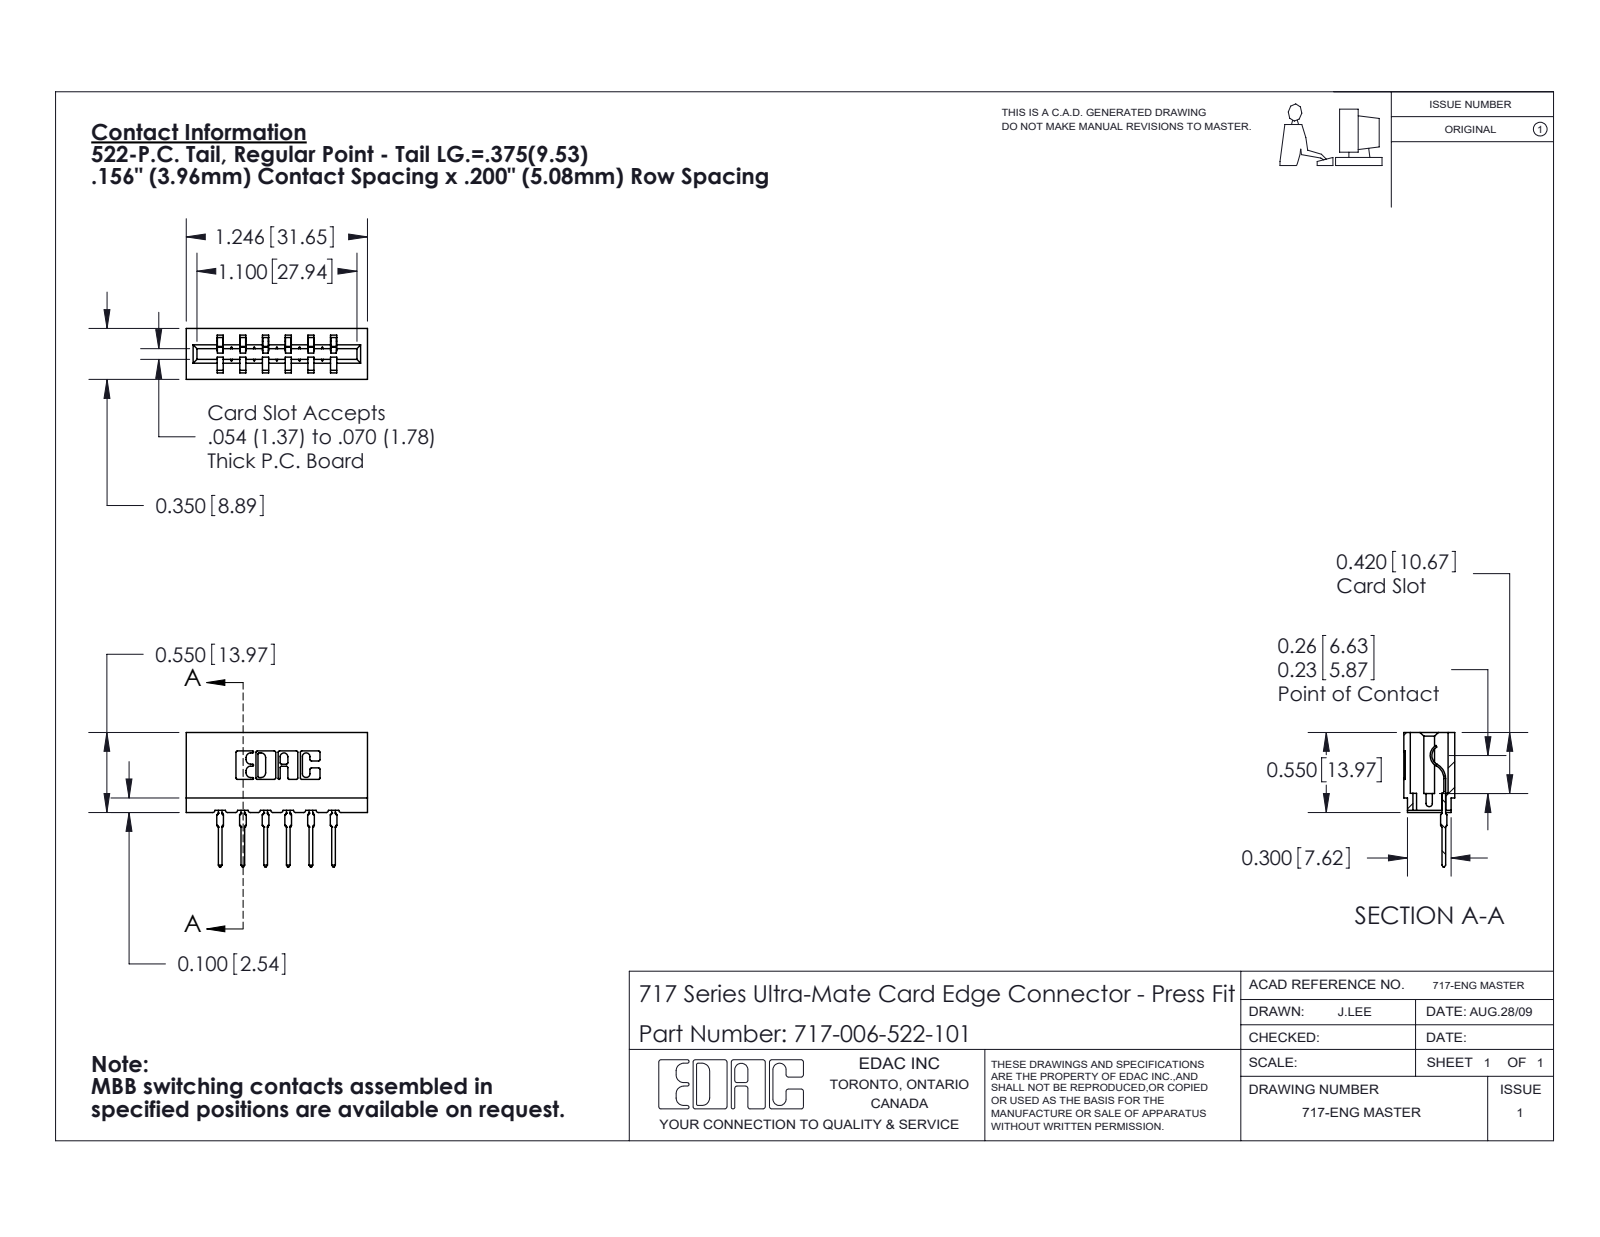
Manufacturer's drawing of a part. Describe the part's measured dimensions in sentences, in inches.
The part is named "717 Part_Insulator Option - 06; 745-292-001_522; 717-006-522-101". Its 3-D file was written by "SolidWorks 2020 (CONFIG_CONTROL_DESIGN)". It is 7 solids with 772 faces: 462 planar, 154 cylindrical and 156 other. Overall it measures 1.246 by 0.924 by 0.35 inches. Its volume is 0.173 cubic inches and its surface area 5.594 square inches. Partial cylindrical surfaces (rounded edges, fillets, slot ends): 22 of radius 0.01, 12 of radius 0.015, 12 of radius 0.021, 6 of radius 0.007, 6 of radius 0.031, 4 of radius 0.005, 4 of radius 0.011, 3 of radius 0.026. The main face-to-face distances are 0.212, 0.156, 0.138, 0.35, 0.198, 0.312, 0.624, 0.042, 0.312, 0.468.
